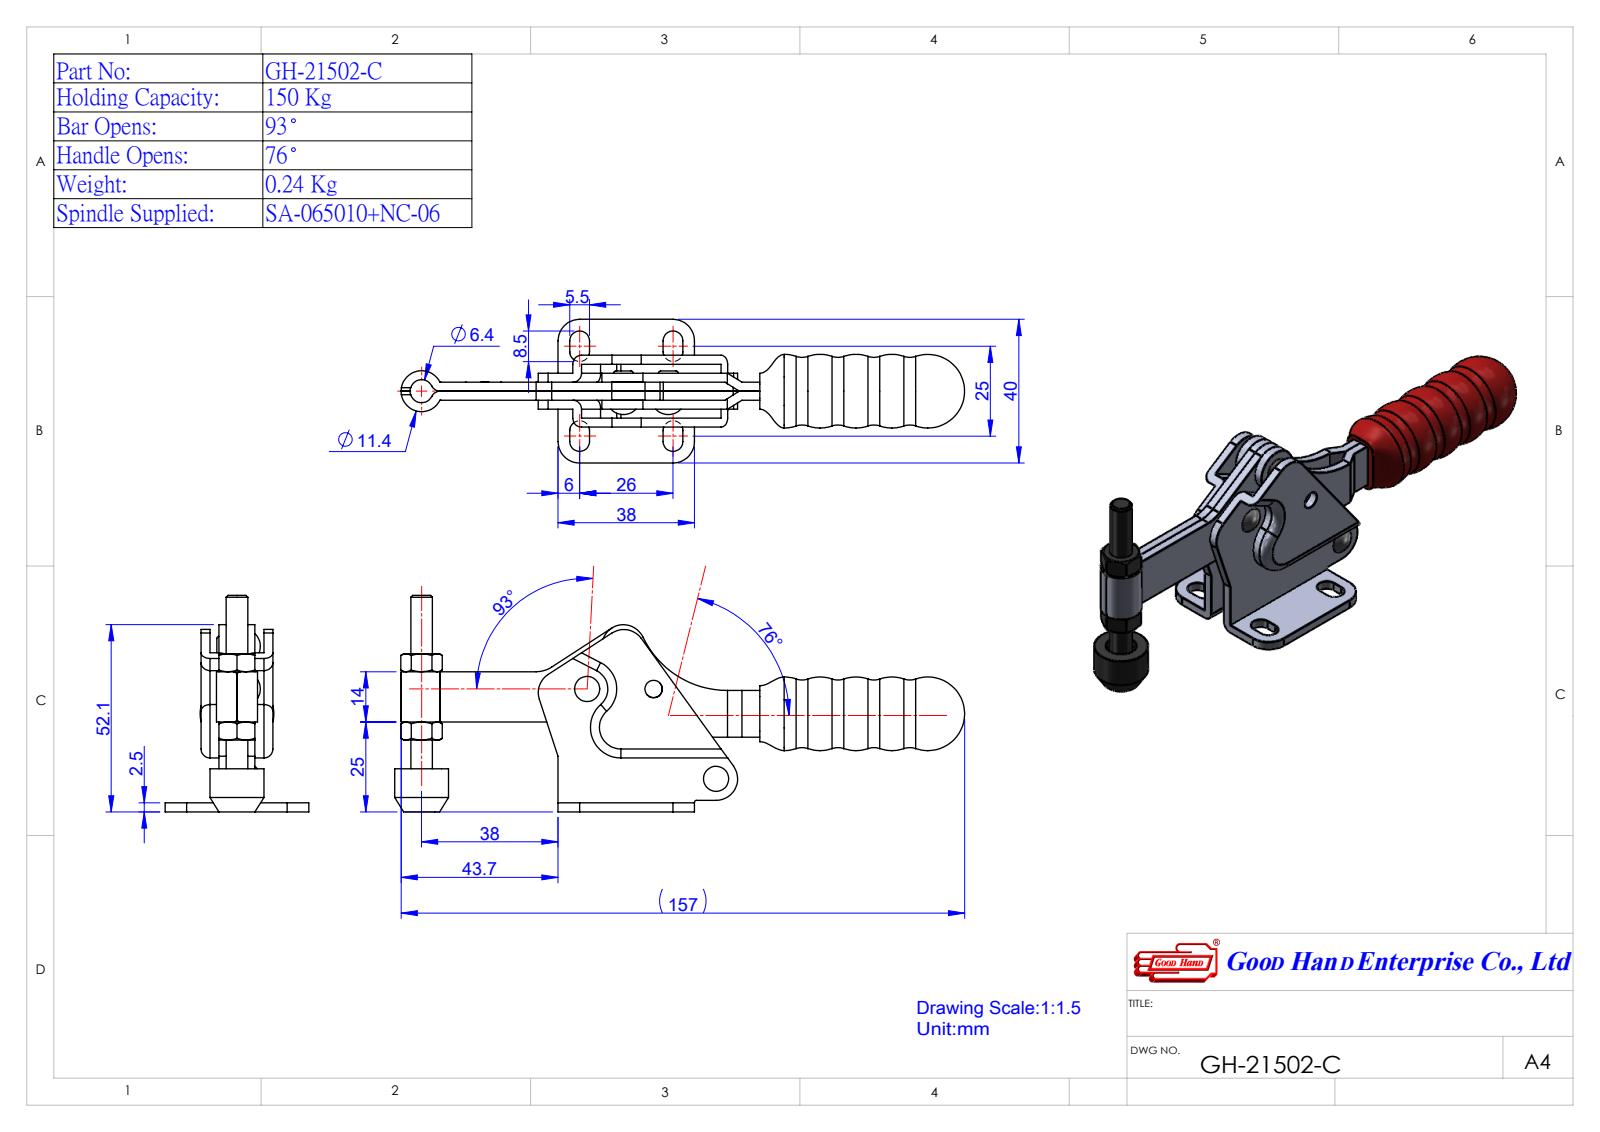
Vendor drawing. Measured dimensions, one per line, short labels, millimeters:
name: GH-21502-C(簡化); Group1^GH-21502-C(簡化); Group2^GH-21502-C(簡化); Group4^GH-21502-C(簡化) (+2 more)
written by: SolidWorks 2016 (AUTOMOTIVE_DESIGN)
unit: mm
bodies: 5 solids, 293 faces (102 planar, 119 cylindrical, 72 other)
size: 157.5 × 60.25 × 40
volume: 44 671 mm³; area: 26 295 mm²
holes: 4× ⌀3, 2× ⌀4.85, 1× ⌀4.8, 1× ⌀6.4
bosses: 1× ⌀15, 1× ⌀11.4, 1× ⌀6
rounds: 10× R6, 8× R2.75, 7× R1, 2× R2.51, 2× R8, 1× R0.5, 1× R5.75, 1× R8.25
face distances: 2.5, 5, 7.5, 12.5, 10, 15, 17.5, 20, 22.5, 25
hole spacings: 8.46, 14.57, 15.61, 18.5, 22.06, 22.99, 23.78, 30.46
